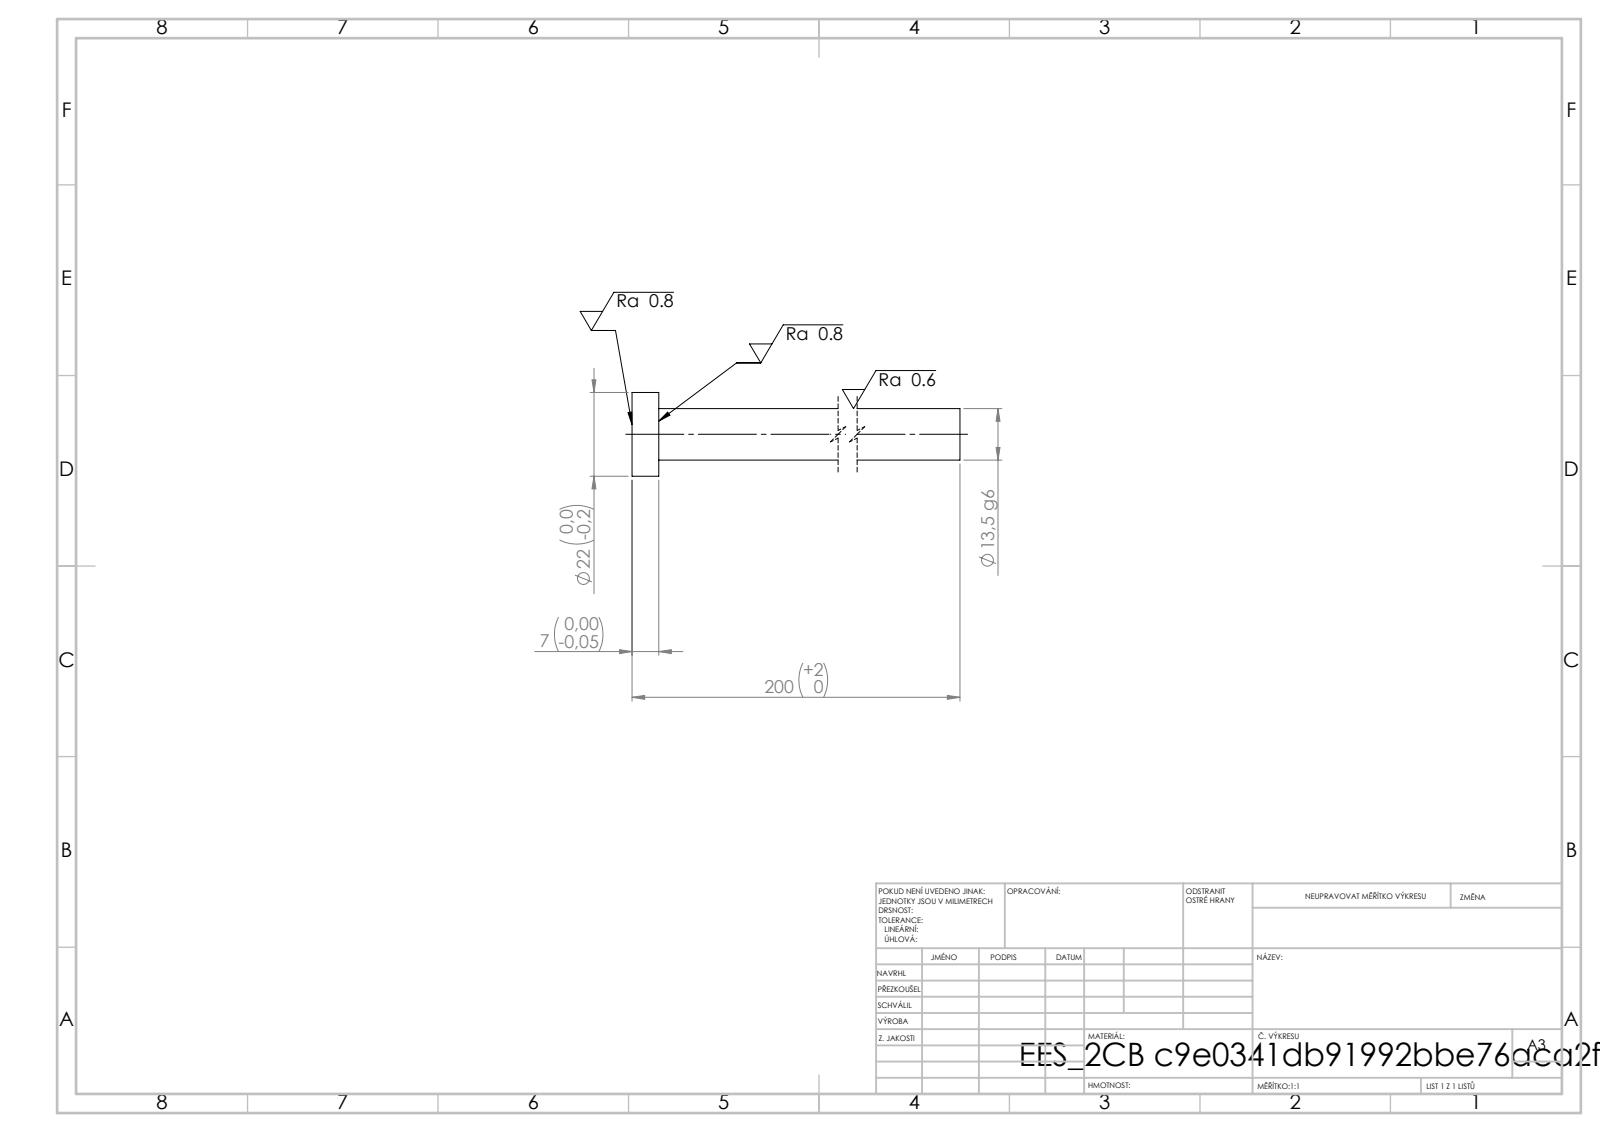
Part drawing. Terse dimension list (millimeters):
written by: SolidWorks 2019 (CONFIG_CONTROL_DESIGN)
unit: mm
bodies: 1 solid, 7 faces (3 planar, 4 cylindrical, 0 other)
size: 200 × 22 × 22
volume: 30 287 mm³; area: 9 429 mm²
bosses: 1× ⌀22, 1× ⌀13.5
face distances: 7, 200, 193
